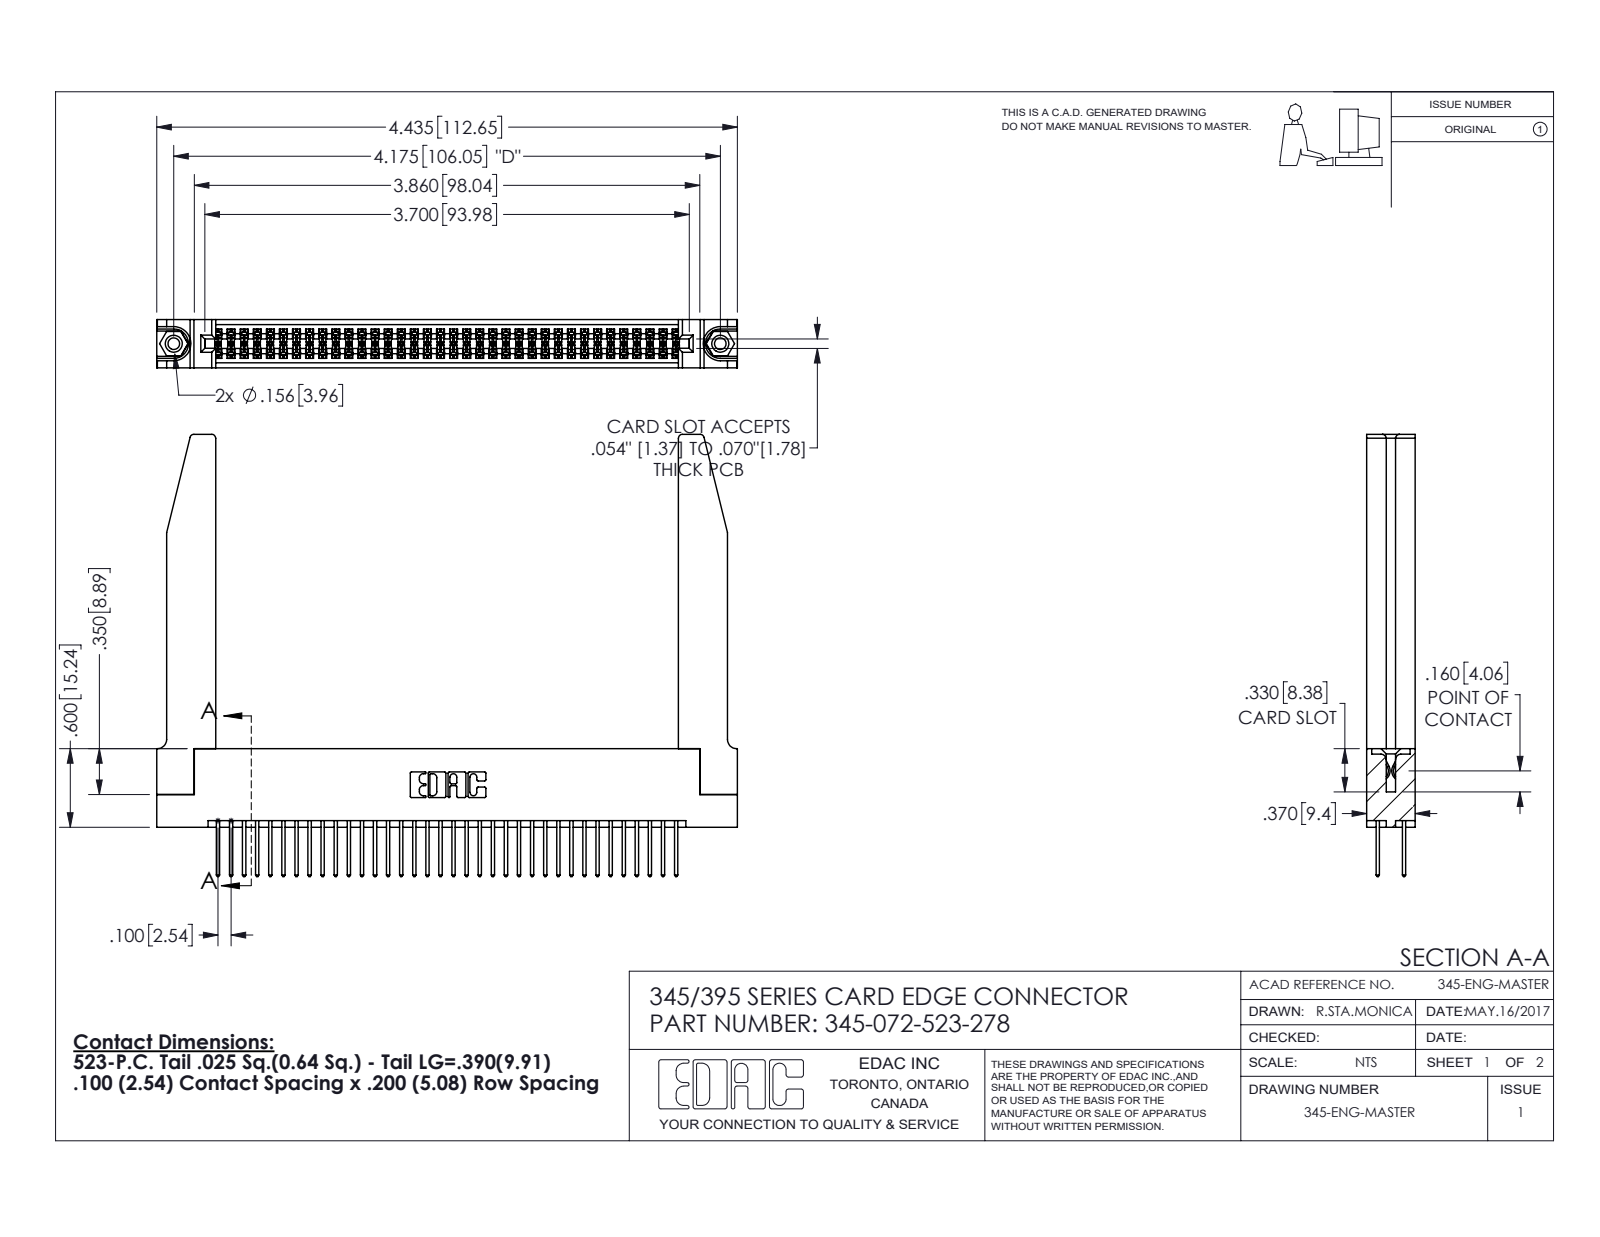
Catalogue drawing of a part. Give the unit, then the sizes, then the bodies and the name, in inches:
Units: inches
Overall size (bounding box): 4.436 × 3.377 × 0.37
Round holes (diameter × count): ⌀0.089 ×2, ⌀0.125 ×2, ⌀0.156 ×2, ⌀0.064 ×1
Round bosses / shafts (diameter × count): ⌀0.155 ×2
Partial cylindrical surfaces — rounded edges, fillets, slot ends (radius × count): R0.006 ×108, R0.01 ×72, R0.01 ×22, R0.03 ×8, R0.007 ×6, R0.031 ×6, R0.026 ×3, R0.014 ×2
Main face-to-face distances: 0.072, 0.37, 0.298, 0.2, 0.098, 0.272, 0.025, 0.225, 0.175, 0.148
Hole centre spacings: 0.27, 3.939, 4.175
Volume: 1.148 in³ · Surface area: 36.73 in²
Bodies: 77 solids, 3960 faces (2598 planar, 1310 cylindrical, 52 other)
Part name (STEP PRODUCT): 345-250-001_345-250-001-102; 345-220-078_345-220-078; 345 Part_Flush Mounting Lugs - 0.156 Dia-TH; 345-292-001_345-293-123 (+1 more)
STEP written by: SolidWorks 2016 (CONFIG_CONTROL_DESIGN)
